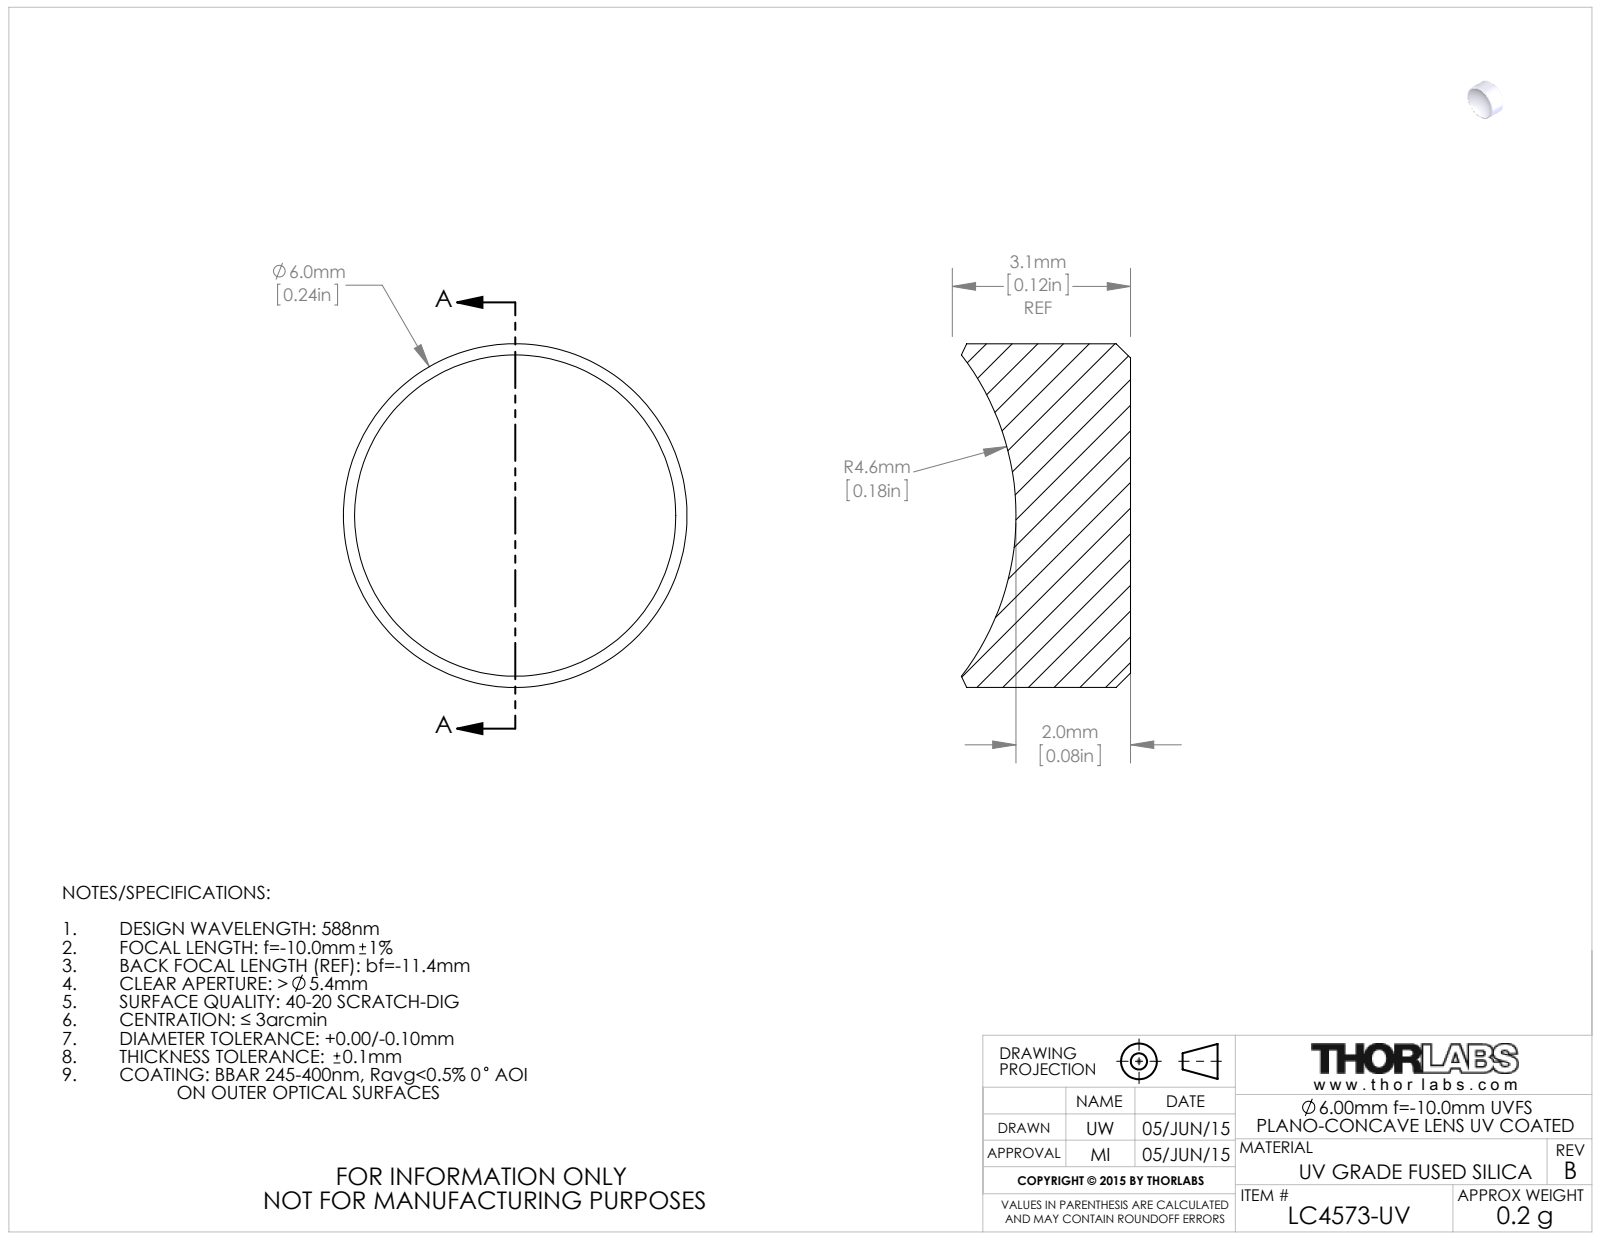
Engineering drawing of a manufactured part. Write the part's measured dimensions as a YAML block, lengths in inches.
part_name: "4341-E0W"
step_written_by: "SolidWorks 2014 (CONFIG_CONTROL_DESIGN)"
units: inches
bodies: {solids: 1, faces: 9, planar: 1, cylindrical: 2, other: 6}
overall_size: [0.236, 0.236, 0.116]
volume: 0.004
surface_area: 0.172
round_bosses_or_shafts:
  - {diameter: 0.236, count: 1}
